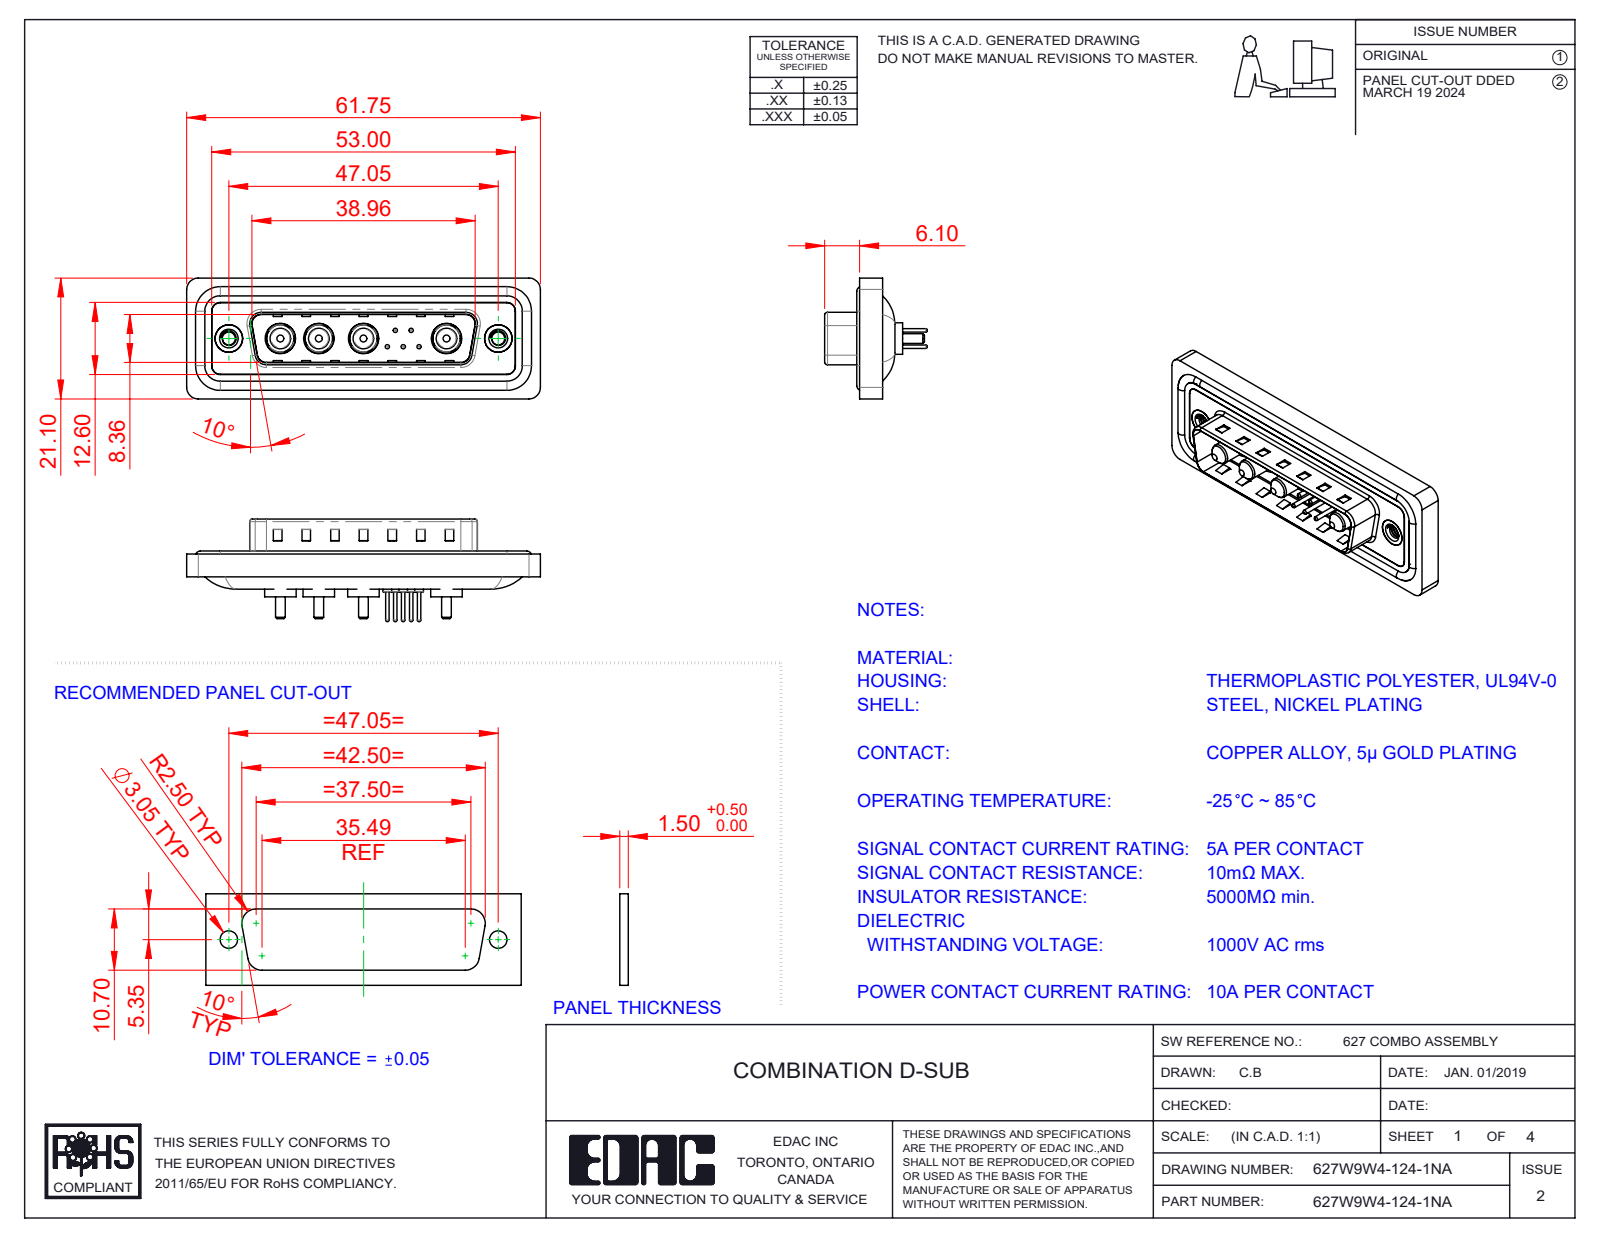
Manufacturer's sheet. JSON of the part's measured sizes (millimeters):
{"part_name": "627Combo Contact Row 2_24; 627Combo Threaded Rivet_A; 627Combo Shell Rear_25 Contacts; 627Combo Contact Row 1_24 (+5 more)", "step_written_by": "SolidWorks 2023 (CONFIG_CONTROL_DESIGN)", "units": "millimeters", "bodies": {"solids": 20, "faces": 822, "planar": 284, "cylindrical": 336, "other": 202}, "overall_size": [61.75, 21.1, 17.9], "volume_mm3": 7347, "surface_area_mm2": 11782, "round_holes": [[0.75, 5], [1.6, 5], [2, 5], [4.85, 4], [5.3, 4], [2.26, 2], [4, 2], [4.8, 2], [5, 2]], "round_bosses_or_shafts": [[1.5, 5], [0.6, 5], [5.5, 4], [5.2, 4], [4.75, 4], [3.75, 4], [3.6, 4], [1.7, 4]], "partial_cylinders_radius": [[1.5, 22], [2, 18], [0.5, 8], [1.6, 8], [0.25, 4], [0.6, 4], [0.65, 4], [0.9, 4]], "face_to_face_distances": [0.4, 1.5, 1.1, 0.5, 3.1, 1.6, 2.9, 0.82, 9.58, 5.65], "hole_center_spacings": [3.16, 2.77, 5.04, 14.51, 2.78, 4.4, 4.41, 5]}
